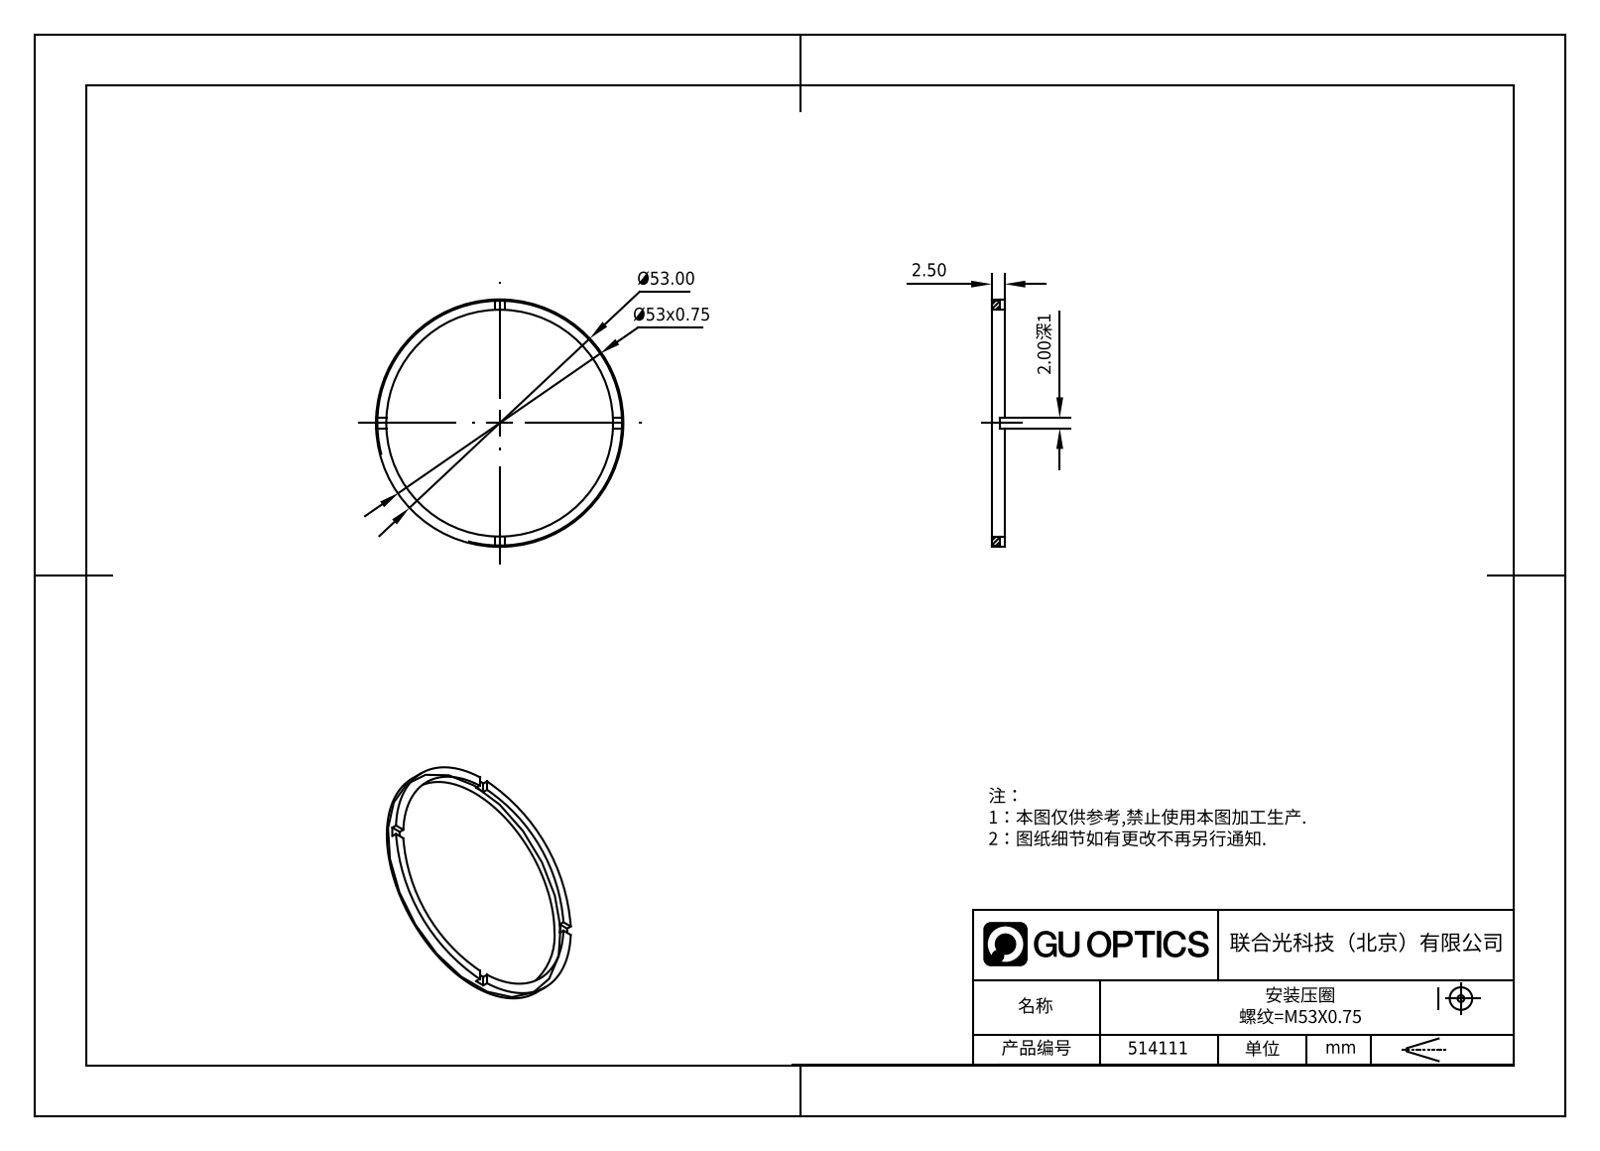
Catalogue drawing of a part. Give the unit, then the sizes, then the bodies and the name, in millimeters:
Units: millimetres
Overall size (bounding box): 53 × 53 × 2.5
Round holes (diameter × count): ⌀48 ×1
Round bosses / shafts (diameter × count): ⌀53 ×1
Main face-to-face distances: 2.5, 1.5, 1, 2
Volume: 972 mm³ · Surface area: 1 591 mm²
Bodies: 1 solid, 21 faces (17 planar, 4 cylindrical, 0 other)
Part name (STEP PRODUCT): 514111
STEP written by: SolidWorks 2020 (CONFIG_CONTROL_DESIGN)
